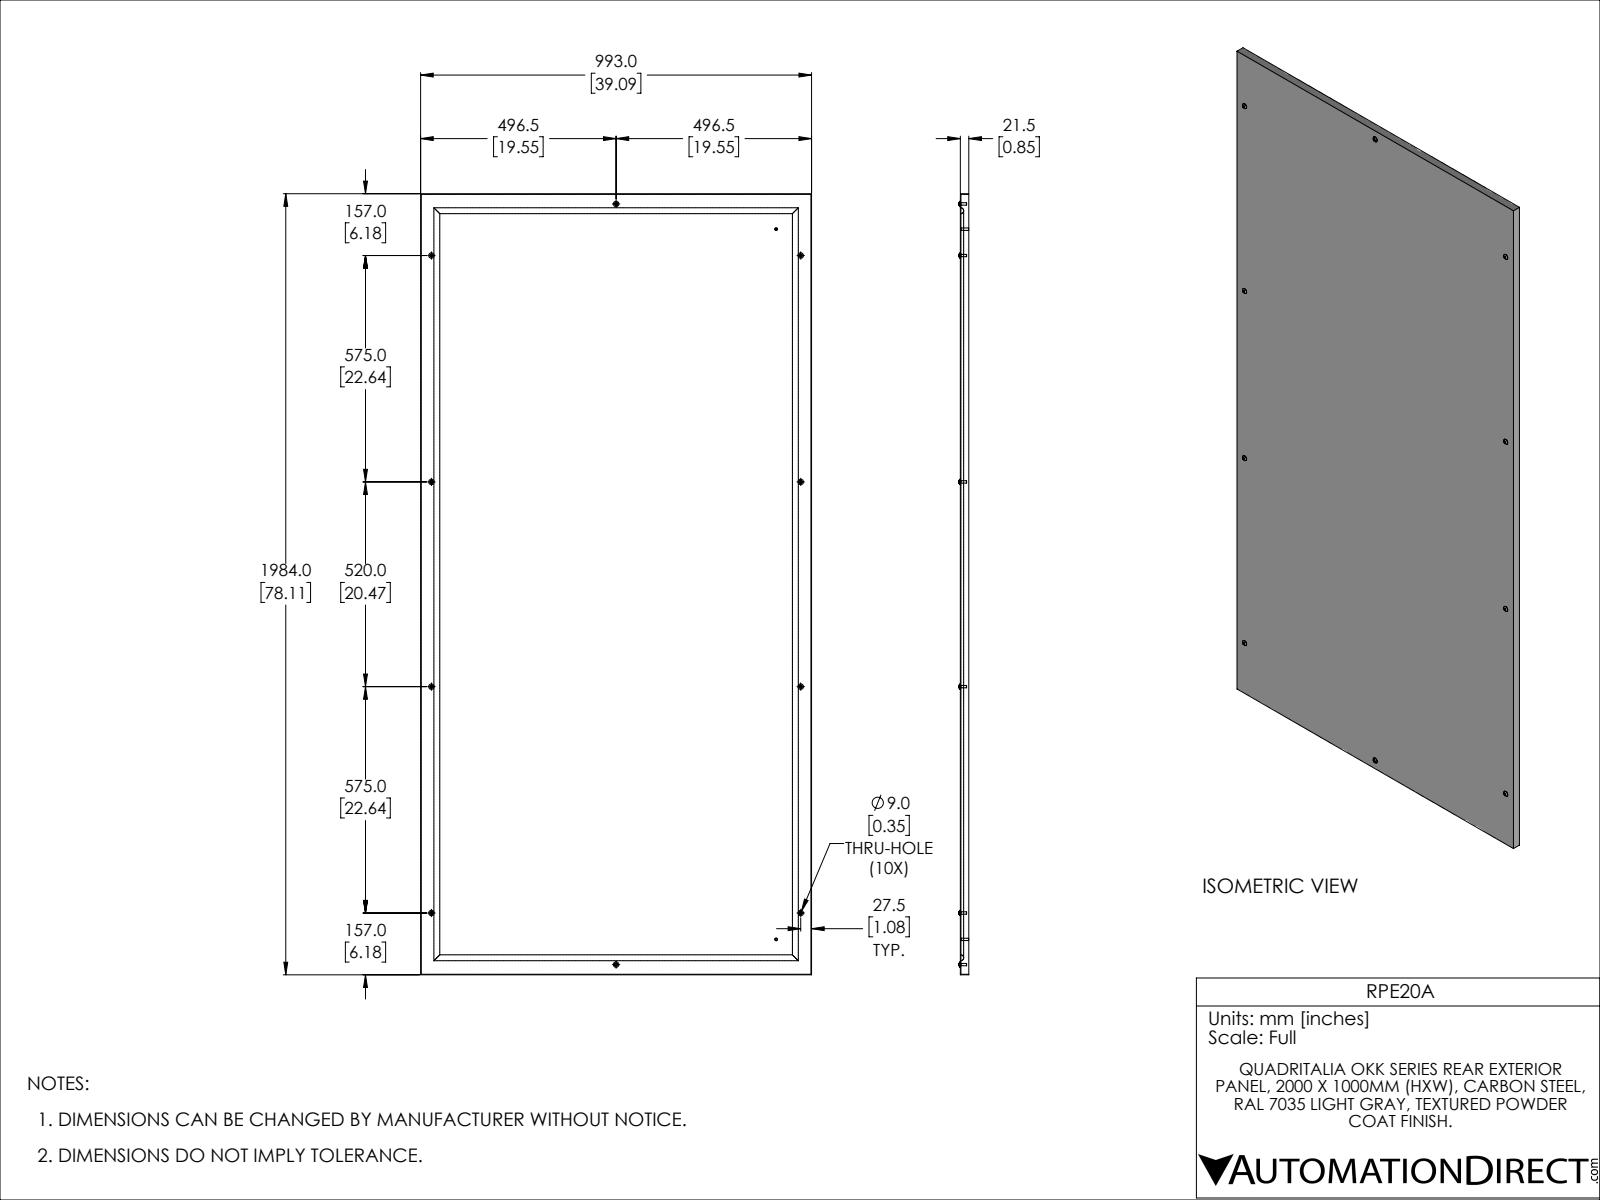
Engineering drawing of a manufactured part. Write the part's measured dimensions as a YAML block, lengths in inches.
part_name: "RPE20A"
step_written_by: "SolidWorks 2021 (CONFIG_CONTROL_DESIGN)"
units: inches
bodies: {solids: 17, faces: 379, planar: 189, cylindrical: 158, other: 32}
overall_size: [78.11, 39.094, 0.992]
volume: 219.5
surface_area: 6830
round_holes:
  - {diameter: 0.354, count: 10}
round_bosses_or_shafts:
  - {diameter: 0.236, count: 12}
  - {diameter: 0.551, count: 10}
  - {diameter: 0.276, count: 2}
partial_cylinders:
  - {radius: 0.02, count: 120}
  - {radius: 0.296, count: 4}
face_to_face_distances: [0.059, 39.035, 39.094, 38.976, 78.051, 78.11, 77.992, 0.846, 0.787, 27.472]
hole_center_spacings: [19.171, 22.638, 33.369, 36.929, 43.11, 43.315, 51.679, 56.765]
